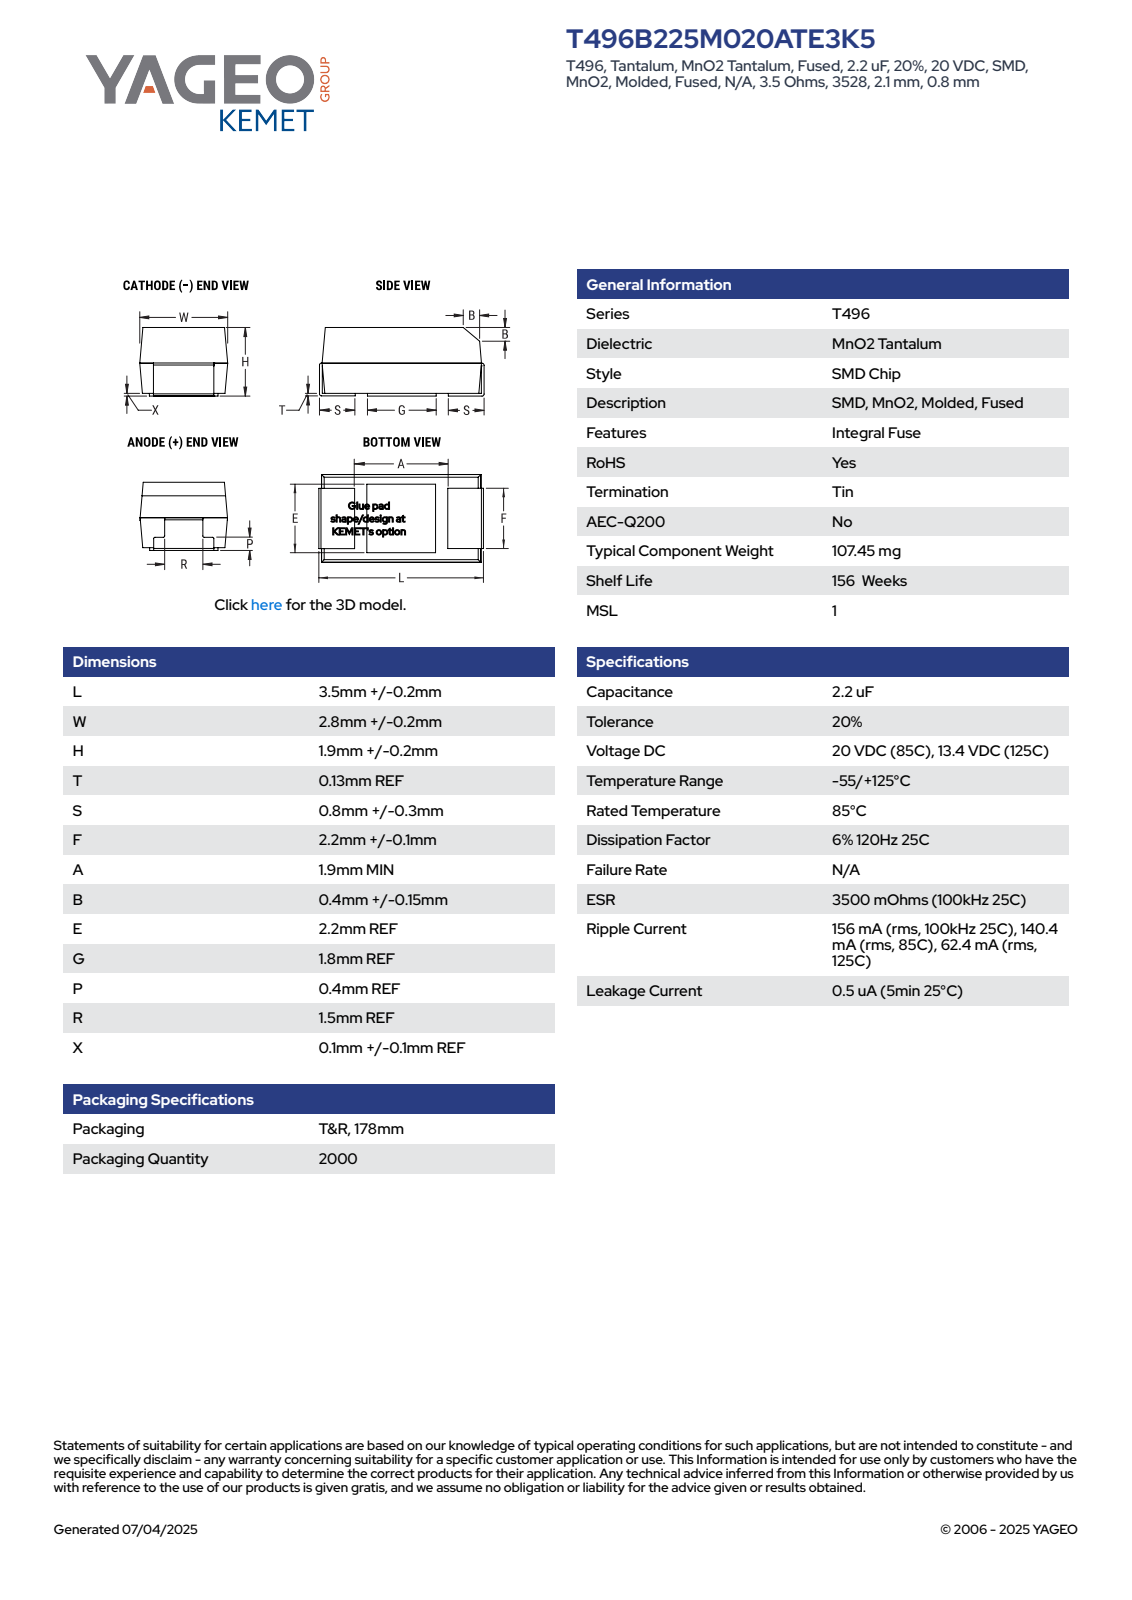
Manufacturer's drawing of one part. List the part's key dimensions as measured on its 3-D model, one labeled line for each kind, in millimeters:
Part name (STEP PRODUCT): Case_Anode_19; Case_Bottom_19; Case_Top_19; Case_Cathode_19 (+1 more)
STEP written by: SolidWorks 2014 (AUTOMOTIVE_DESIGN)
Units: millimetres
Bodies: 4 solids, 43 faces (38 planar, 5 cylindrical, 0 other)
Overall size (bounding box): 3.7 × 3 × 2.1
Volume: 20 mm³ · Surface area: 80 mm²
Main face-to-face distances: 0.9, 1.97, 1.07, 2.98, 3.43, 2.1, 1.03, 3.57, 1, 2.07
